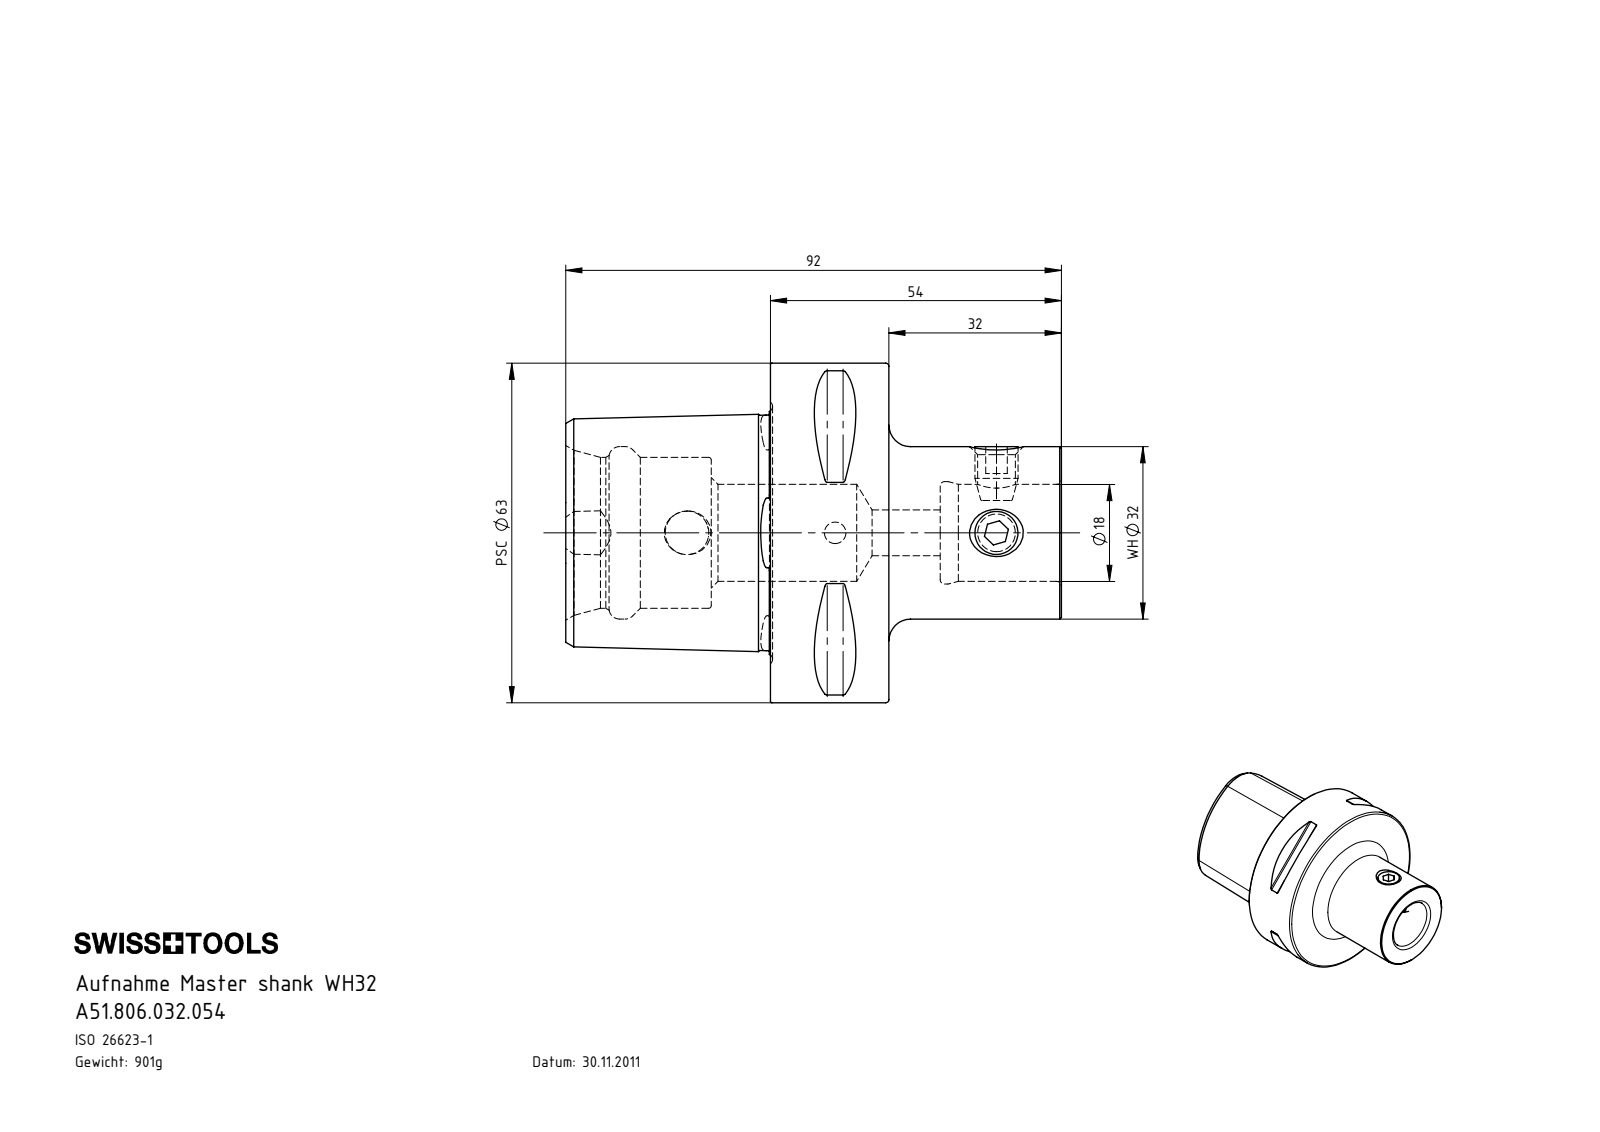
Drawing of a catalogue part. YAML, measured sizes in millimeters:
part_name: "PS6-WH3.K01.054_B; WH2-ER1.001.010; A51.806.032.054"
step_written_by: "SolidWorks 2022 (AUTOMOTIVE_DESIGN)"
units: millimeters
bodies: {solids: 3, faces: 177, planar: 39, cylindrical: 41, other: 97}
overall_size: [92, 63, 63]
volume: 115389
surface_area: 25384
round_holes:
  - {diameter: 7, count: 2}
  - {diameter: 4, count: 1}
  - {diameter: 8.1, count: 1}
  - {diameter: 8.5, count: 1}
  - {diameter: 18, count: 1}
  - {diameter: 19, count: 1}
  - {diameter: 28, count: 1}
  - {diameter: 32, count: 1}
round_bosses_or_shafts:
  - {diameter: 8, count: 2}
  - {diameter: 63, count: 1}
partial_cylinders:
  - {radius: 0.5, count: 8}
  - {radius: 6, count: 1}
face_to_face_distances: [22, 54, 32, 38, 60, 92, 24.88, 27, 11, 33]
hole_center_spacings: [27.5, 29.95, 57.45]
